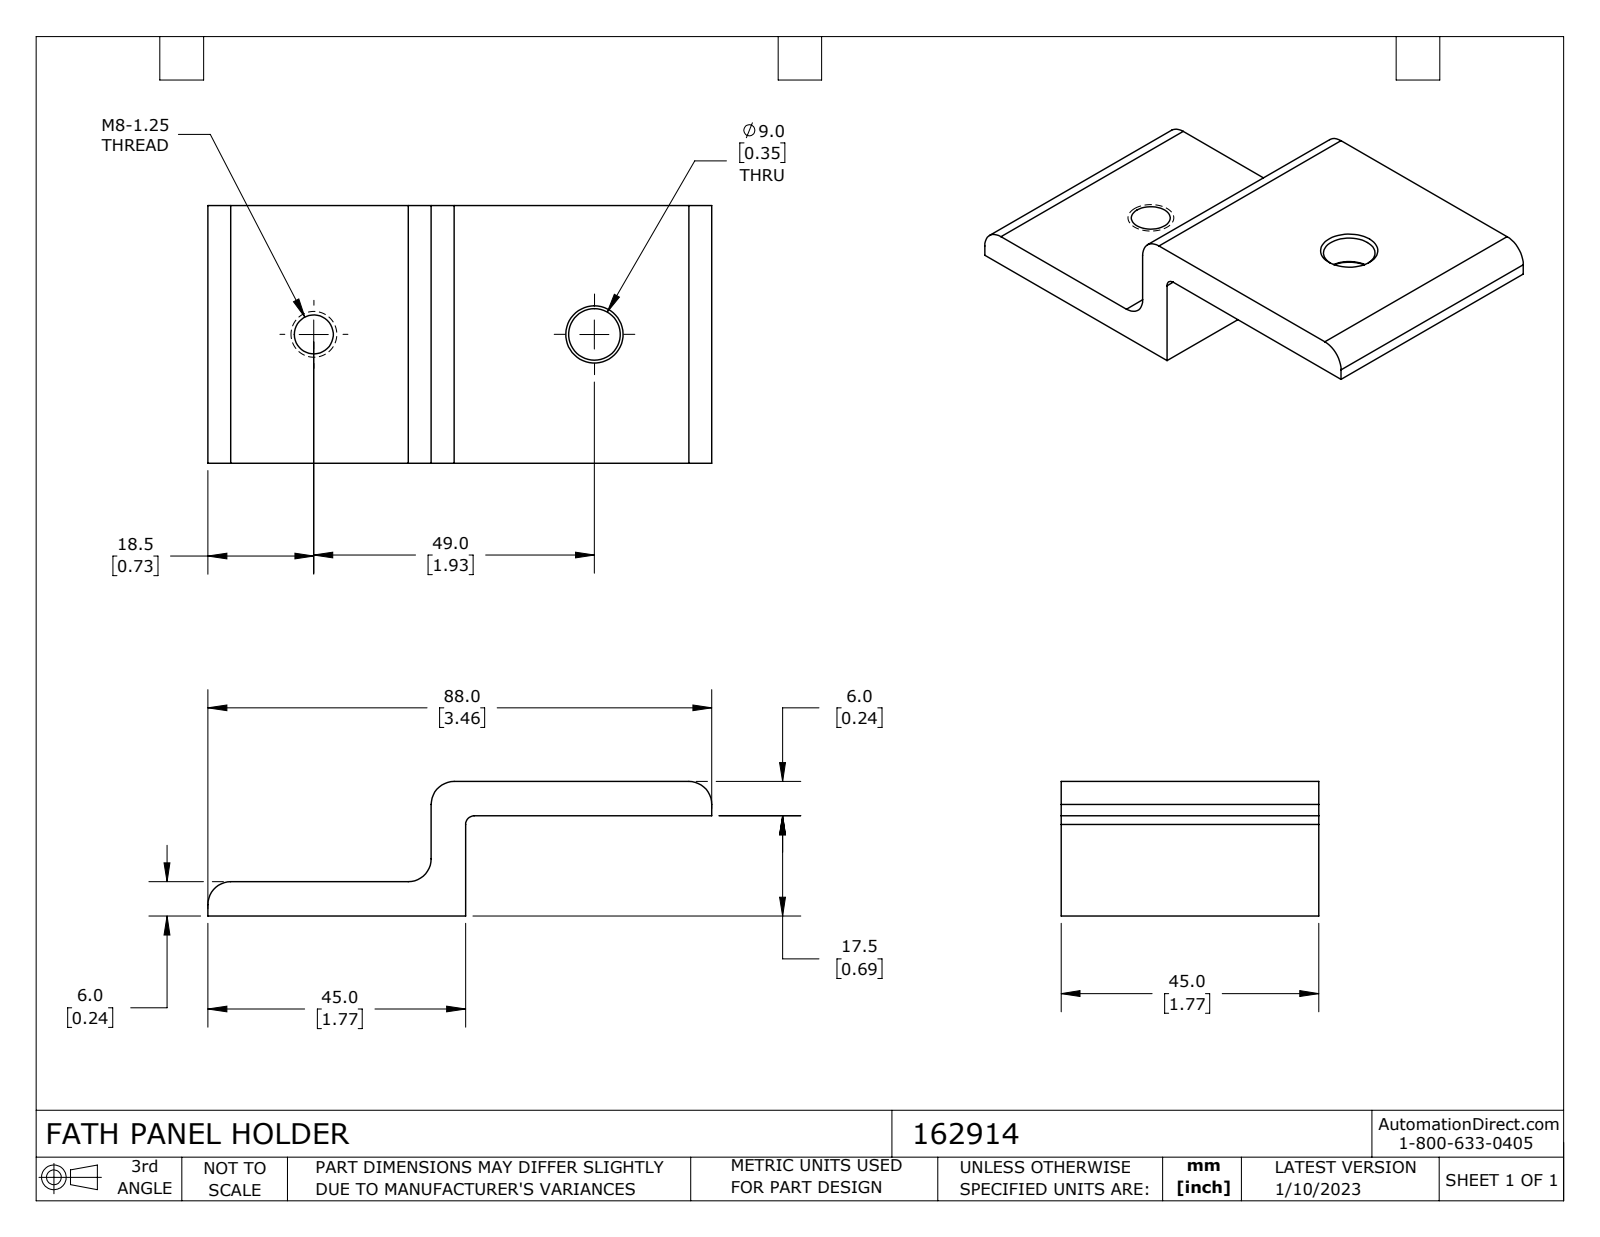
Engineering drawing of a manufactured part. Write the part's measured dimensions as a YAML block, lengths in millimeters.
part_name: "162914"
step_written_by: "SolidWorks 2021 (CONFIG_CONTROL_DESIGN)"
units: millimeters
bodies: {solids: 1, faces: 23, planar: 10, cylindrical: 9, other: 4}
overall_size: [88, 45, 23.5]
volume: 27600
surface_area: 11030
round_holes:
  - {diameter: 6.8, count: 1}
  - {diameter: 9, count: 1}
partial_cylinders:
  - {radius: 4, count: 4}
  - {radius: 1.5, count: 1}
face_to_face_distances: [6, 17.5, 23.5, 11.5, 45, 39, 43, 49, 88]
hole_center_spacings: [49]
